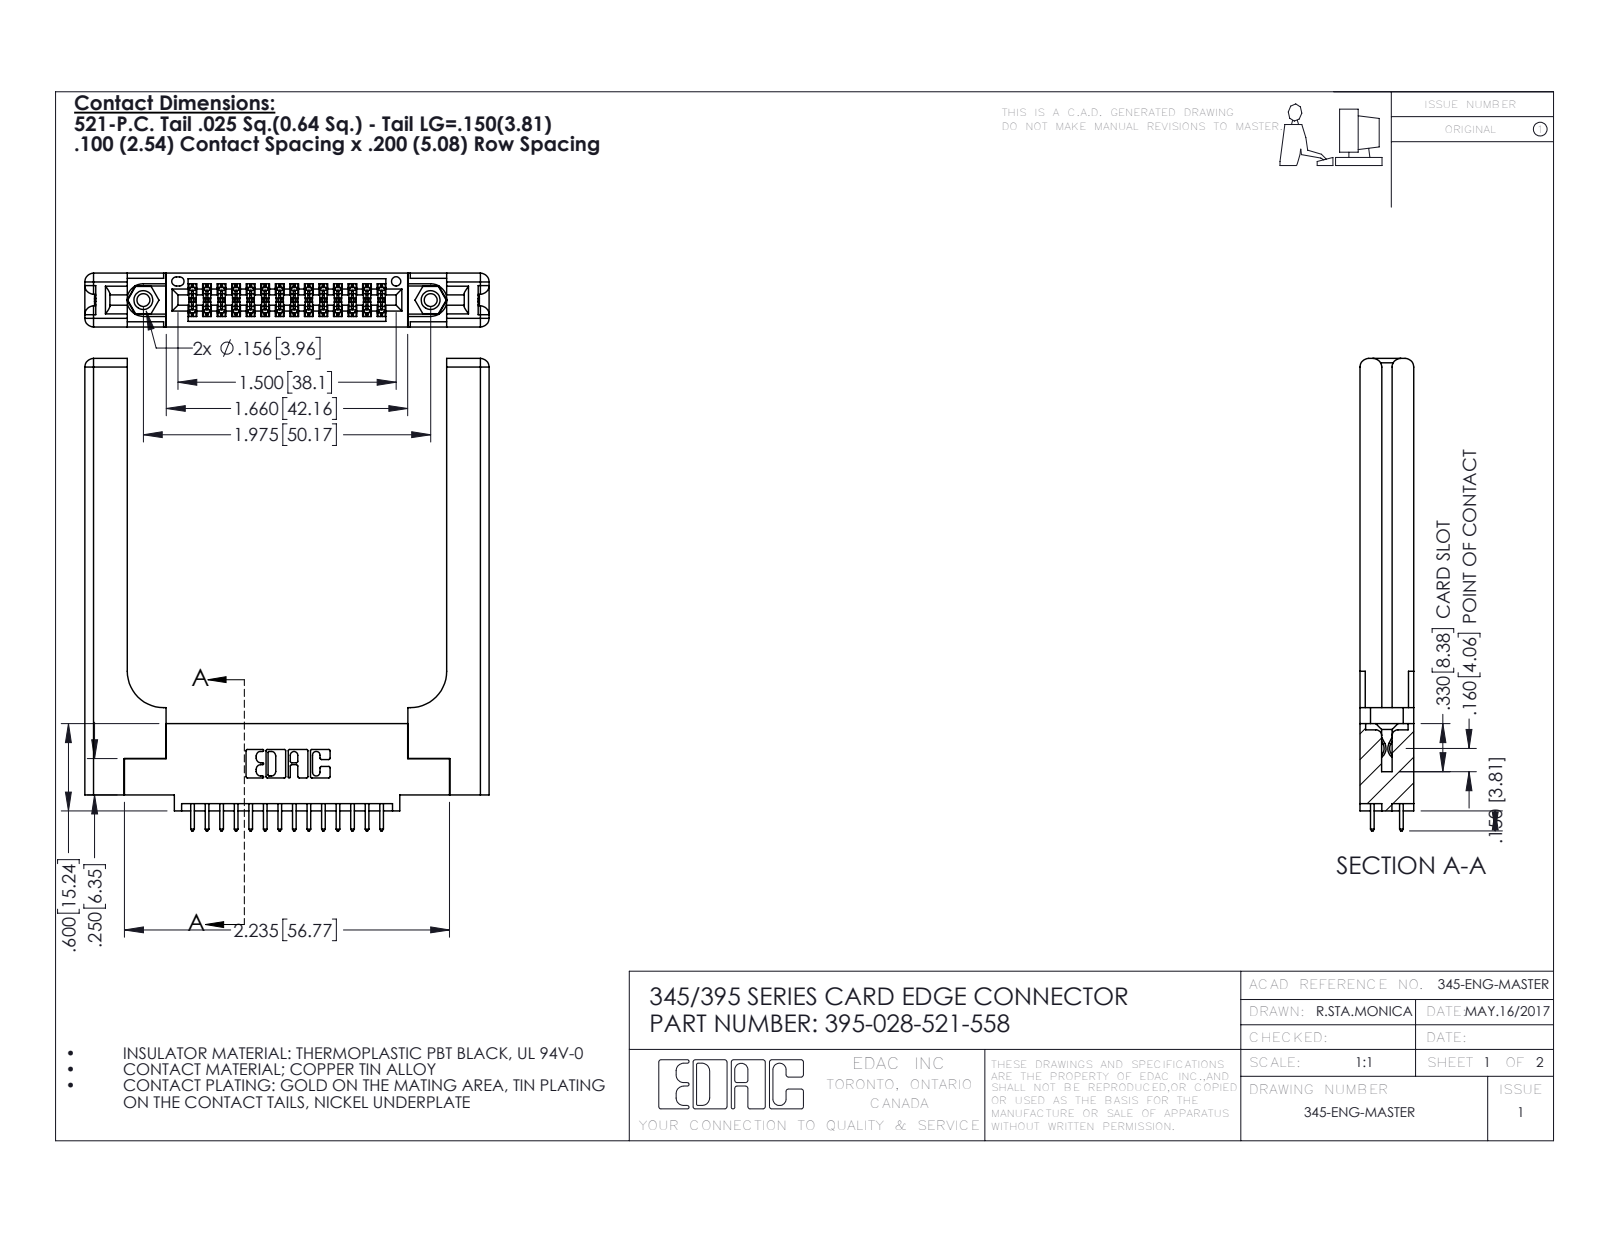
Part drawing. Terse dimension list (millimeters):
name: 345-220-058_345-220-058; 395-028-521-558; 345-292-001_345-293-121; 345 Part_0.110 Offset - 0.156 Dia-TH (+1 more)
written by: SolidWorks 2016 (CONFIG_CONTROL_DESIGN)
unit: mm
bodies: 33 solids, 1786 faces (1156 planar, 570 cylindrical, 60 other)
size: 82.5 × 70.6 × 9.4
volume: 15 000 mm³; area: 14 160 mm²
holes: 2× ⌀2.3, 2× ⌀3.2, 2× ⌀4, 1× ⌀1.6
bosses: 2× ⌀3.9
rounds: 42× R0.2, 28× R0.3, 22× R0.3, 16× R1.5, 6× R0.2, 6× R0.8, 3× R0.7, 2× R0.4
face distances: 9.4, 1.8, 7.6, 3.8, 3.8, 2, 5.6, 5.1, 5.7, 2.5
hole spacings: 6.9, 44.2, 50.2
